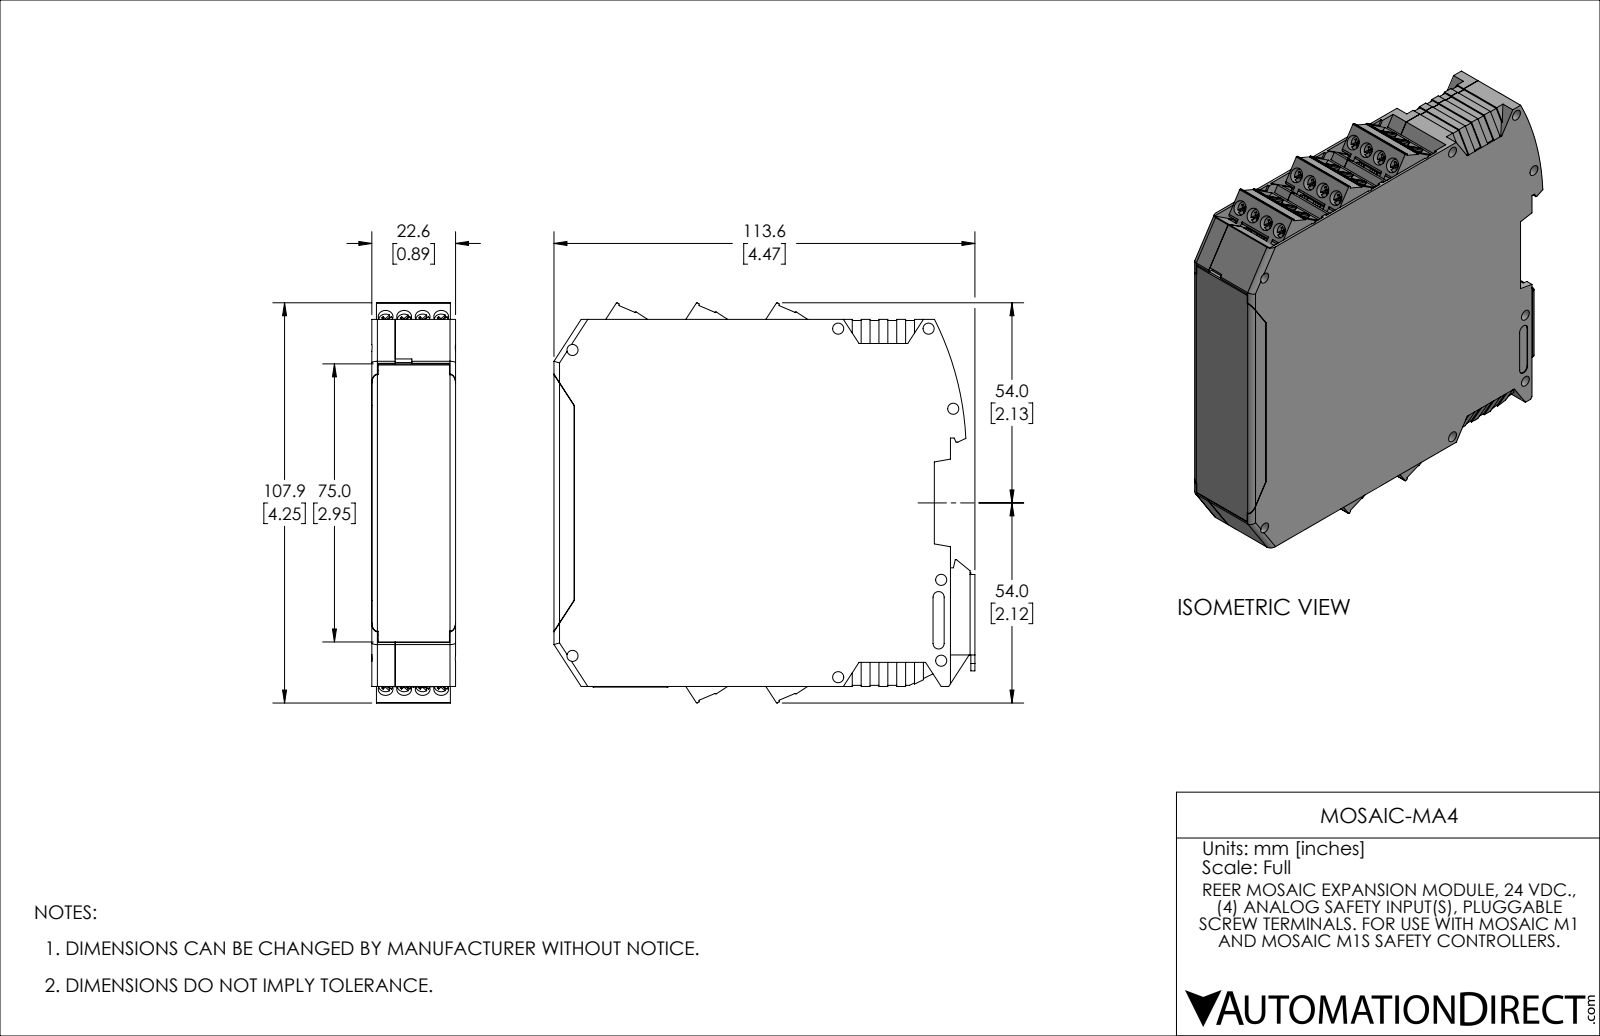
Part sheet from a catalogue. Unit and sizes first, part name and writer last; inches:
Units: inches
Overall size (bounding box): 4.472 × 4.25 × 0.89
Round holes (diameter × count): ⌀0.055 ×22, ⌀0.11 ×20, ⌀0.157 ×20, ⌀0.118 ×14, ⌀0.063 ×1
Round bosses / shafts (diameter × count): ⌀0.149 ×20, ⌀0.177 ×1, ⌀0.11 ×1, ⌀0.053 ×1
Partial cylindrical surfaces — rounded edges, fillets, slot ends (radius × count): R0.012 ×42, R0.114 ×20, R0.03 ×17, R0.008 ×15, R0.059 ×10, R0.02 ×5, R0.024 ×5, R0.039 ×5
Main face-to-face distances: 0.049, 0.841, 0.89, 0.791, 0.713, 0.039, 0.248, 0.03, 0.811, 0.593
Hole centre spacings: 0.197, 0.394, 0.504, 0.74, 0.591, 0.463, 0.608, 0.713
Volume: 3.671 in³ · Surface area: 125 in²
Bodies: 11 solids, 2059 faces (1740 planar, 316 cylindrical, 3 other)
Part name (STEP PRODUCT): MOSAIC-MA4
STEP written by: SolidWorks 2021 (AUTOMOTIVE_DESIGN)
